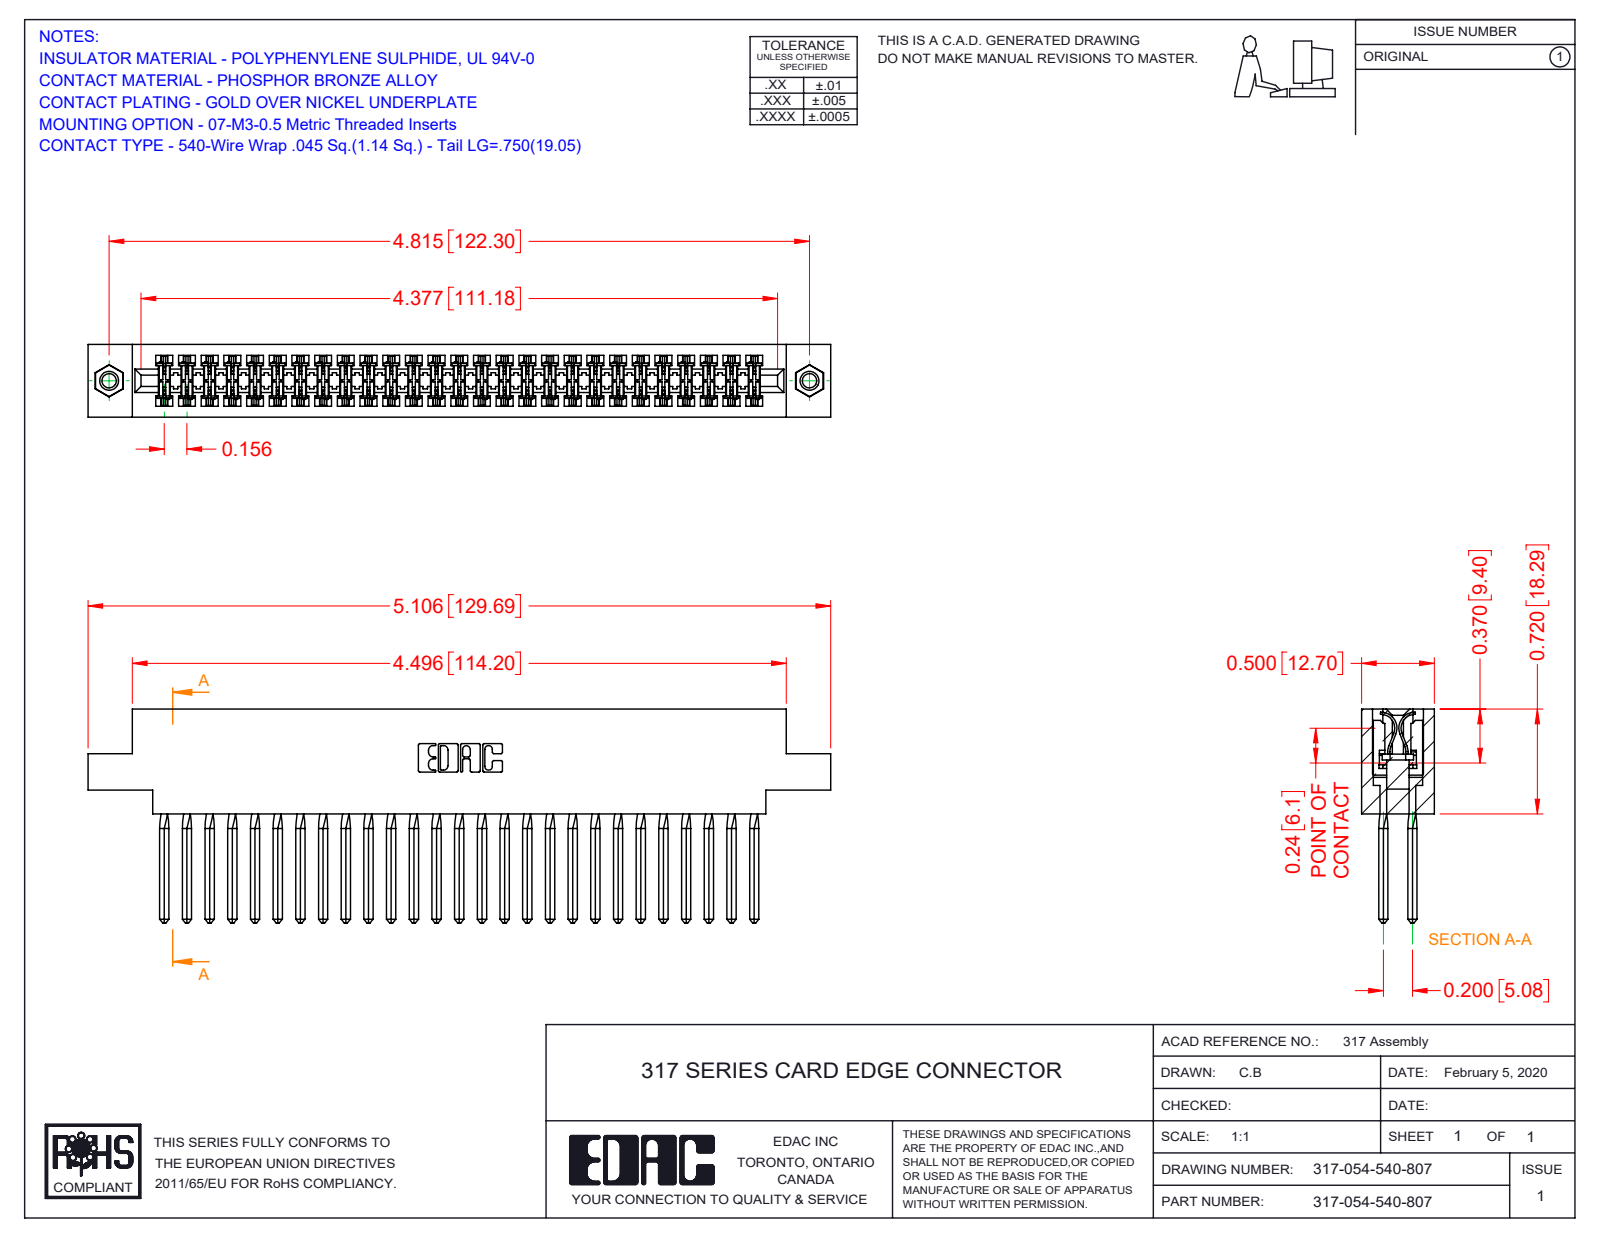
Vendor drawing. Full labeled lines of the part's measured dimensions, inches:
Part name (STEP PRODUCT): 317-290-001_540; 317-054-540-807; 317 Part_.156 Dia - TI; 345-250-001_345-250-005-103
STEP written by: SolidWorks 2016 (CONFIG_CONTROL_DESIGN)
Units: inches
Bodies: 57 solids, 4968 faces (4032 planar, 704 cylindrical, 232 other)
Overall size (bounding box): 5.106 × 1.47 × 0.5
Volume: 1.296 in³ · Surface area: 48.28 in²
Round holes (diameter × count): ⌀0.098 ×2, ⌀0.125 ×2, ⌀0.156 ×2
Round bosses / shafts (diameter × count): ⌀0.155 ×2
Partial cylindrical surfaces — rounded edges, fillets, slot ends (radius × count): R0.015 ×108, R0.01 ×22, R0.007 ×6, R0.031 ×6, R0.026 ×3, R0.095 ×2, R0.1 ×2, R0.11 ×2
Main face-to-face distances: 0.5, 0.075, 0.425, 0.35, 0.11, 0.195, 0.094, 0.2, 0.72, 0.115
Hole centre spacings: 4.815
